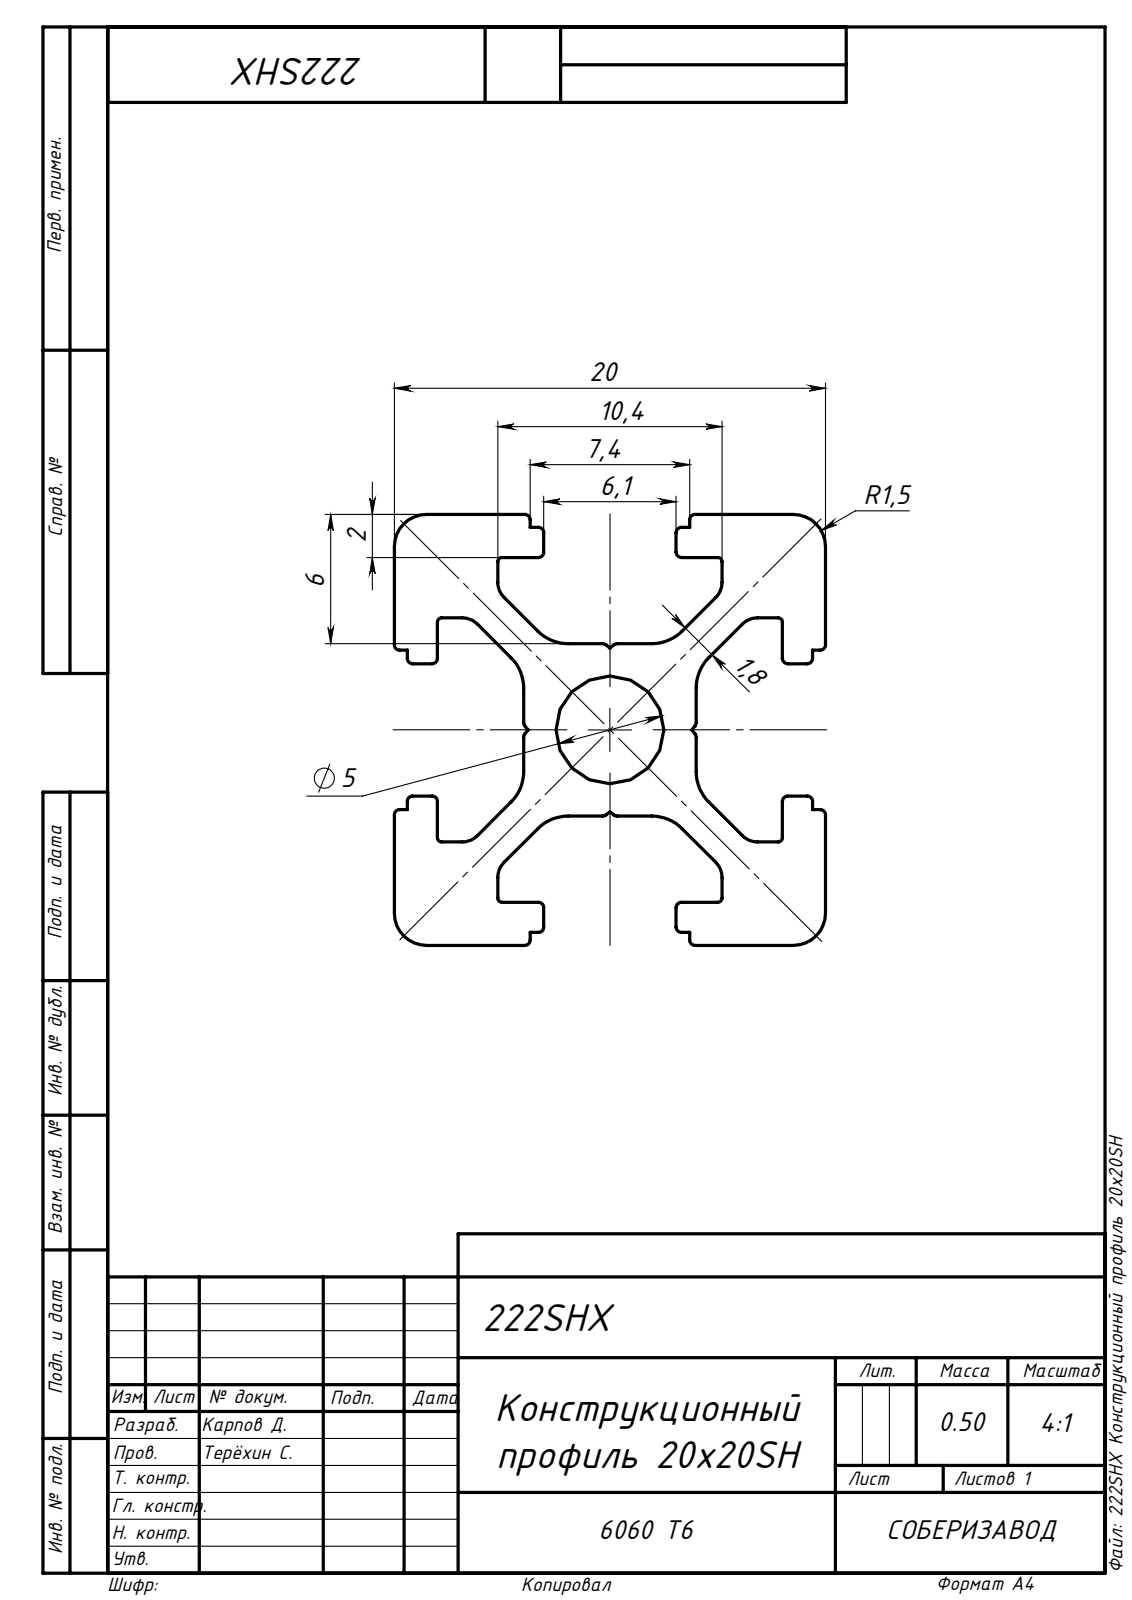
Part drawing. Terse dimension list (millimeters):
written by: SolidWorks 2019 (AUTOMOTIVE_DESIGN)
unit: mm
bodies: 1 solid, 136 faces (74 planar, 62 cylindrical, 0 other)
size: 1000 × 20 × 20
volume: 184 055 mm³; area: 160 371 mm²
holes: 1× ⌀5
rounds: 32× R0.25, 8× R0.2, 8× R1, 8× R2, 4× R1.5
face distances: 20, 18, 2, 6, 14, 4, 12, 1.74, 4.8, 15.2
